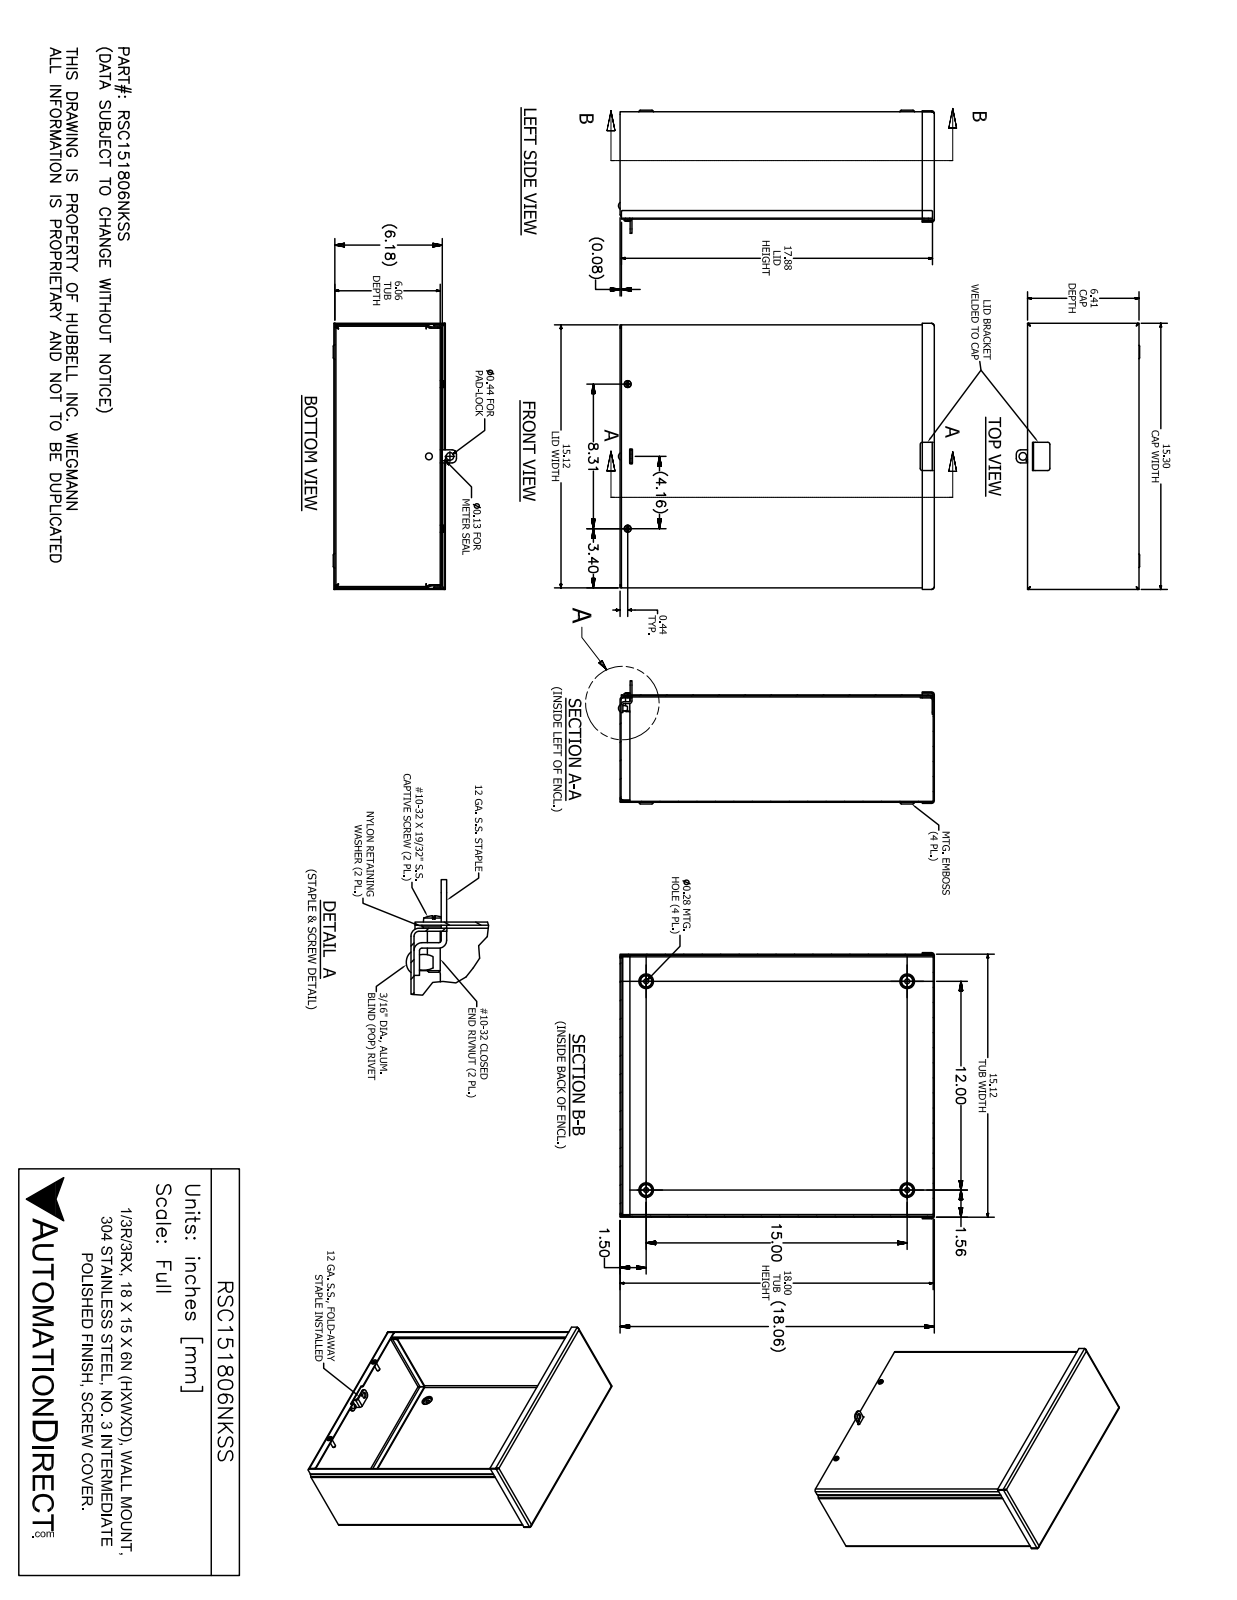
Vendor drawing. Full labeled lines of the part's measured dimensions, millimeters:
Part name (STEP PRODUCT): RSC151806NKSS
STEP written by: SolidWorks 2017 (AUTOMOTIVE_DESIGN)
Units: millimetres
Bodies: 13 solids, 375 faces (199 planar, 99 cylindrical, 77 other)
Overall size (bounding box): 461 × 388.6 × 179.9
Volume: 932 100 mm³ · Surface area: 1 316 000 mm²
Round holes (diameter × count): ⌀6.4 ×4, ⌀7.1 ×4, ⌀4 ×2, ⌀5 ×2, ⌀6.5 ×2, ⌀7.1 ×2, ⌀3.2 ×1, ⌀5 ×1, ⌀5.1 ×1, ⌀11.1 ×1
Round bosses / shafts (diameter × count): ⌀11.5 ×2, ⌀10.3 ×2, ⌀6.3 ×2, ⌀4.2 ×2, ⌀4.7 ×1
Partial cylindrical surfaces — rounded edges, fillets, slot ends (radius × count): R2.4 ×17, R3.9 ×17, R0.8 ×6, R3.2 ×4, R6.4 ×4, R1.6 ×3, R1.2 ×2, R1.3 ×2
Main face-to-face distances: 1.5, 155.4, 156.9, 153.9, 382.5, 457.2, 381, 384, 455.7, 458.7
Hole centre spacings: 54.1, 54.5, 211.2, 259.4, 259.5, 304.8, 381, 410.7
